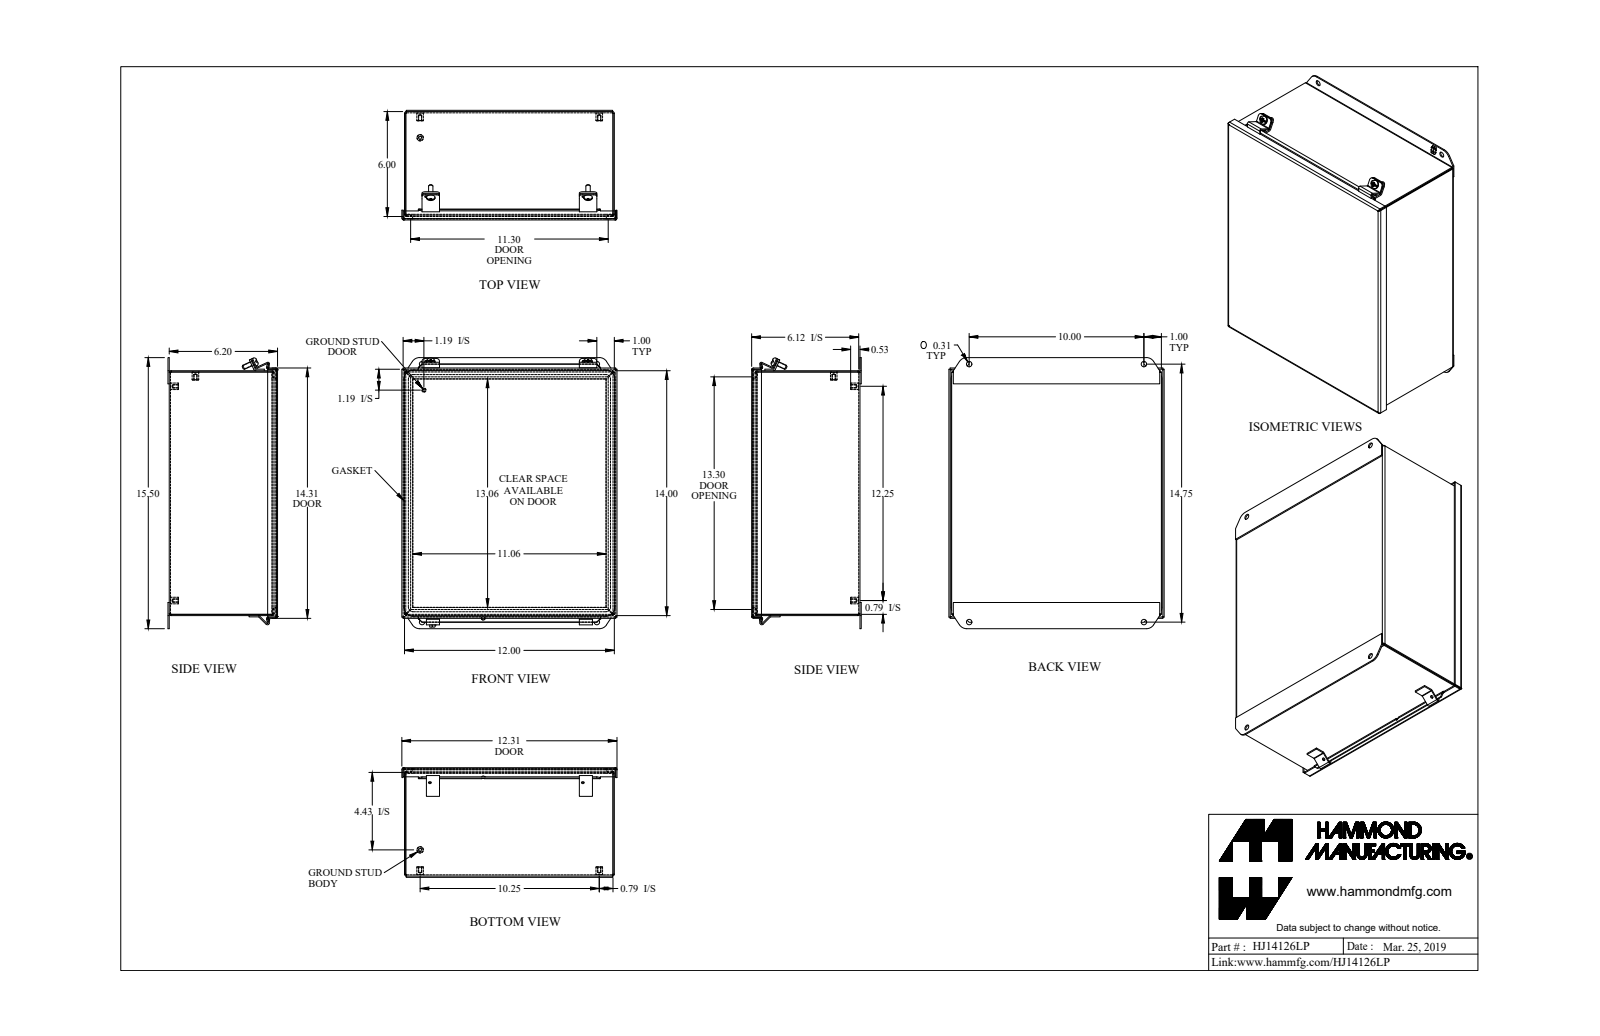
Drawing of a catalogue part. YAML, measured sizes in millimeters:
part_name: "HJ14126LP"
step_written_by: "SolidWorks 2018 (AUTOMOTIVE_DESIGN)"
units: millimeters
bodies: {solids: 19, faces: 627, planar: 341, cylindrical: 160, other: 126}
overall_size: [393.7, 312.7, 159.2]
volume: 947300
surface_area: 1032000
round_holes:
  - {diameter: 4, count: 5}
  - {diameter: 8, count: 4}
  - {diameter: 4, count: 2}
  - {diameter: 5.4, count: 2}
round_bosses_or_shafts:
  - {diameter: 9.5, count: 5}
  - {diameter: 6.4, count: 3}
  - {diameter: 12.2, count: 2}
  - {diameter: 4.8, count: 1}
partial_cylinders:
  - {radius: 0.9, count: 16}
  - {radius: 2.7, count: 16}
  - {radius: 6.4, count: 16}
  - {radius: 3.6, count: 4}
  - {radius: 4.8, count: 4}
  - {radius: 12.7, count: 4}
  - {radius: 12.7, count: 4}
  - {radius: 0.3, count: 2}
face_to_face_distances: [1.8, 155.6, 157.4, 153.7, 303, 353.8, 301.1, 304.8, 355.6, 351.9]
hole_center_spacings: [254, 260.4, 311.2, 405.7, 452.6, 31.5, 31.6, 32.3]
